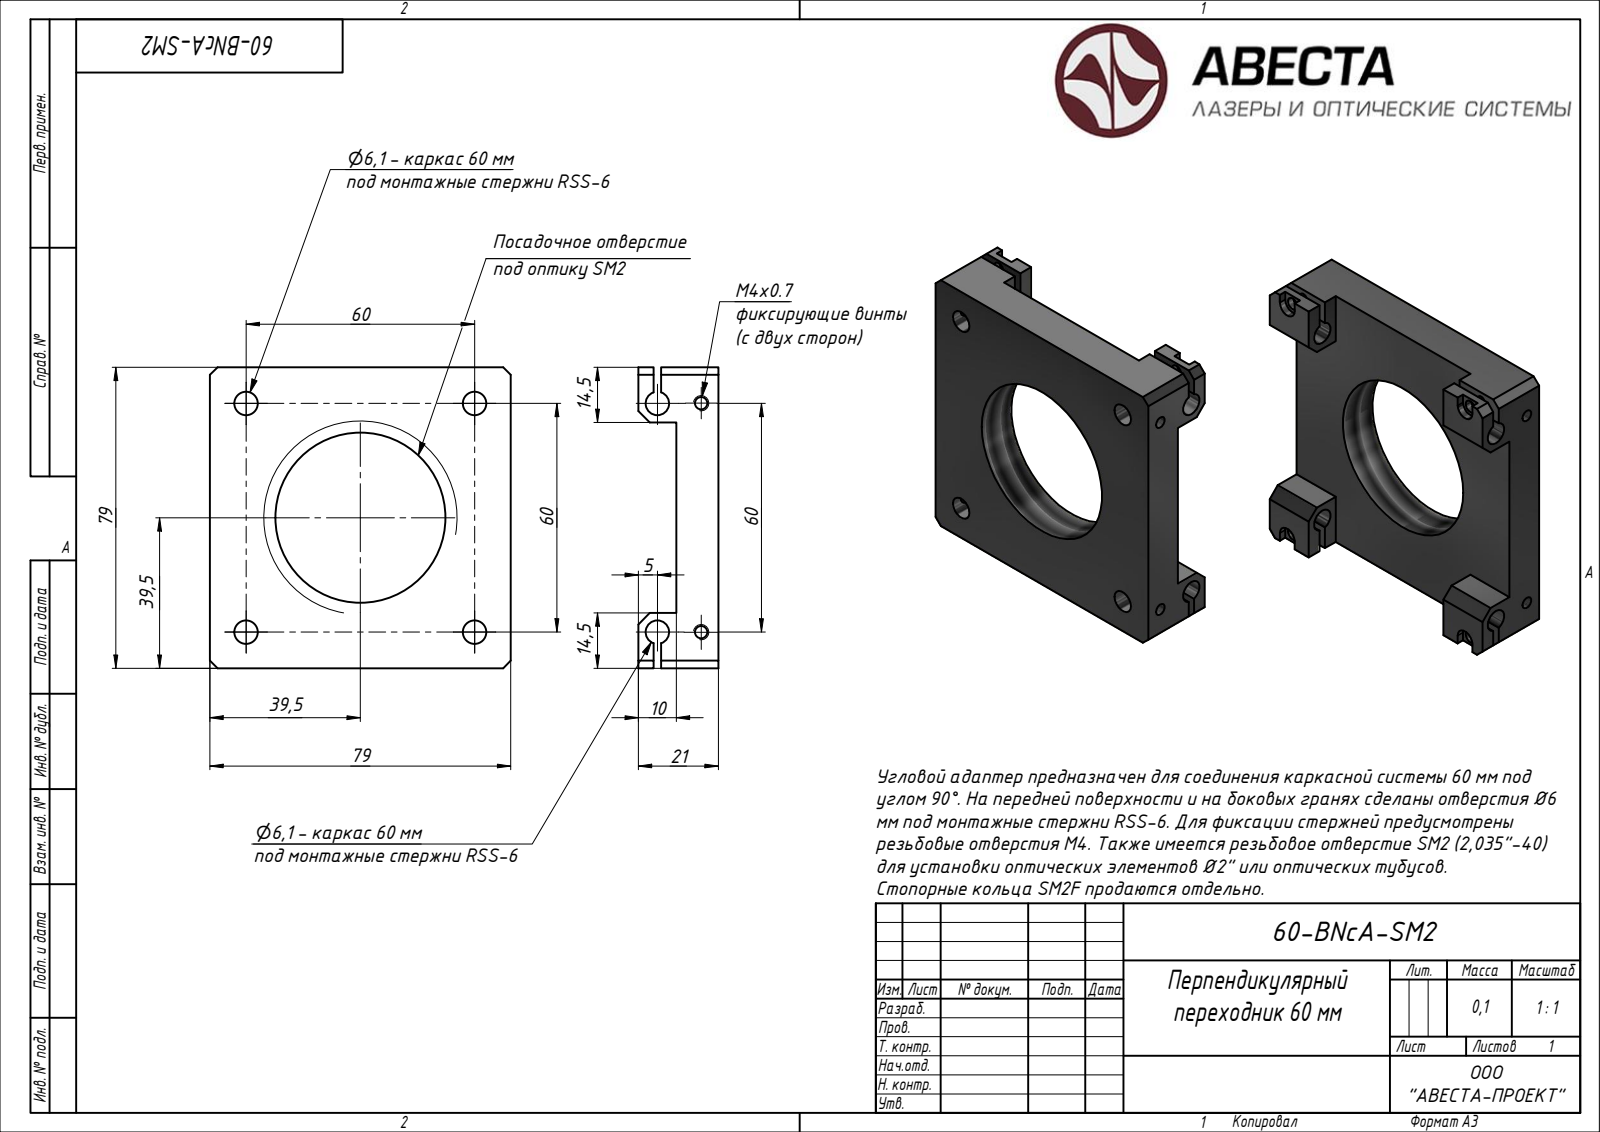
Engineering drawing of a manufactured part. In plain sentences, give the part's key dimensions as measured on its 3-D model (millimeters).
Its 3-D file was written by "ST-DEVELOPER v15 (AUTOMOTIVE_DESIGN)". It is 1 solid with 100 faces: 58 planar, 0 cylindrical and 42 other. Overall it measures 79 by 79 by 21 millimeters. Its volume is 55 532 cubic millimeters and its surface area 19 020 square millimeters. The main face-to-face distances are 11, 79, 14.5, 64.5, 6, 10, 4, 21, 2, 50.
